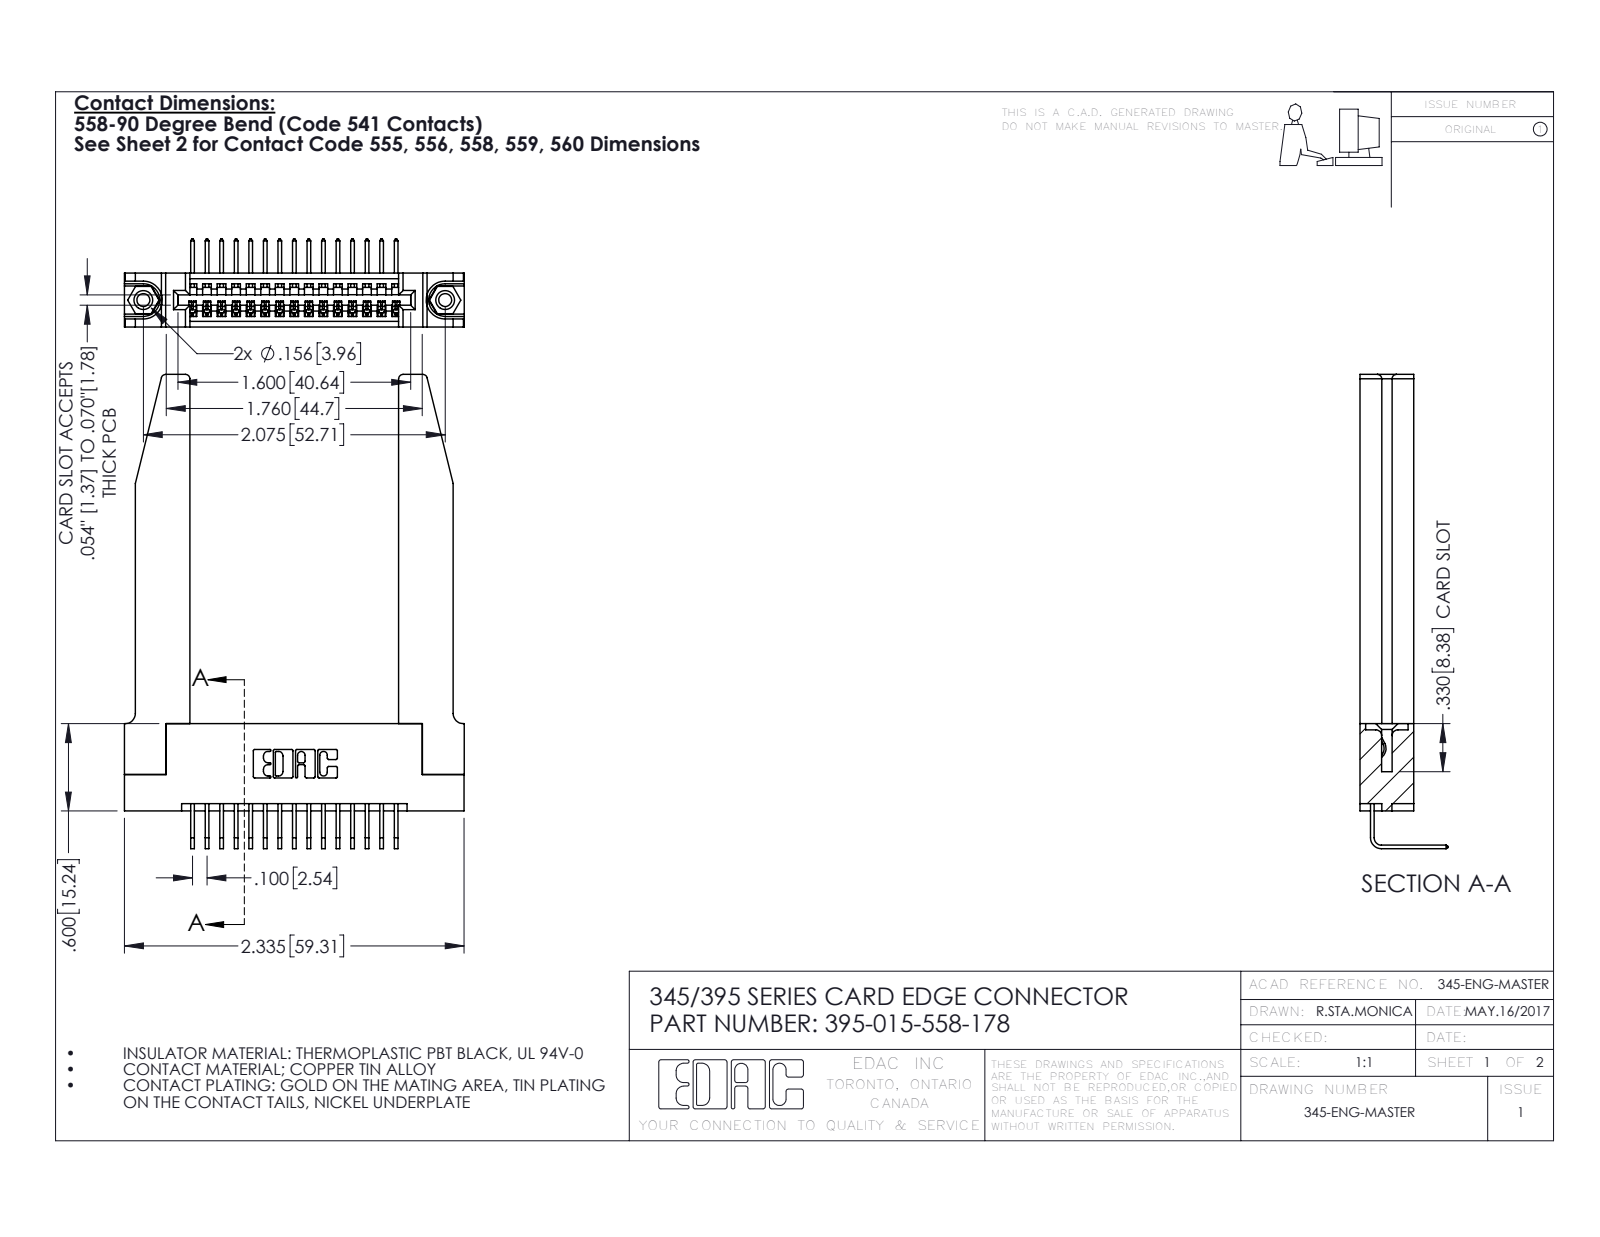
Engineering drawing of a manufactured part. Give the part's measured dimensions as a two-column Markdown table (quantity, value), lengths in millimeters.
| quantity | value |
| --- | --- |
| part name | 345-292-001_558 Tail - 2; 345 Part_Flush Mounting Lugs - 0.156 Dia-TH; 345-220-078_345-220-078; 395-015-558-178 (+1 more) |
| STEP written by | SolidWorks 2016 (CONFIG_CONTROL_DESIGN) |
| units | millimeters |
| bodies | 20 solids, 1260 faces (852 planar, 356 cylindrical, 52 other) |
| overall size | 82.8 × 59.3 × 15.4 |
| volume | 13 200 mm³ |
| surface area | 14 030 mm² |
| round holes (diameter × count) | 2.3 × 2, 3.2 × 2, 4 × 2, 1.6 × 1 |
| round bosses / shafts (diameter × count) | 3.9 × 2 |
| partial cylindrical surfaces (radius × count) | 0.2 × 30, 0.3 × 22, 0.8 × 8, 0.2 × 6, 0.8 × 6, 0.7 × 3, 0.8 × 2, 1 × 2 |
| main face-to-face distances | 9.4, 1.8, 7.6, 5.1, 3.8, 3.8, 2, 5.6, 2.5, 6.9 |
| hole center spacings | 6.9, 46.8, 52.7 |
